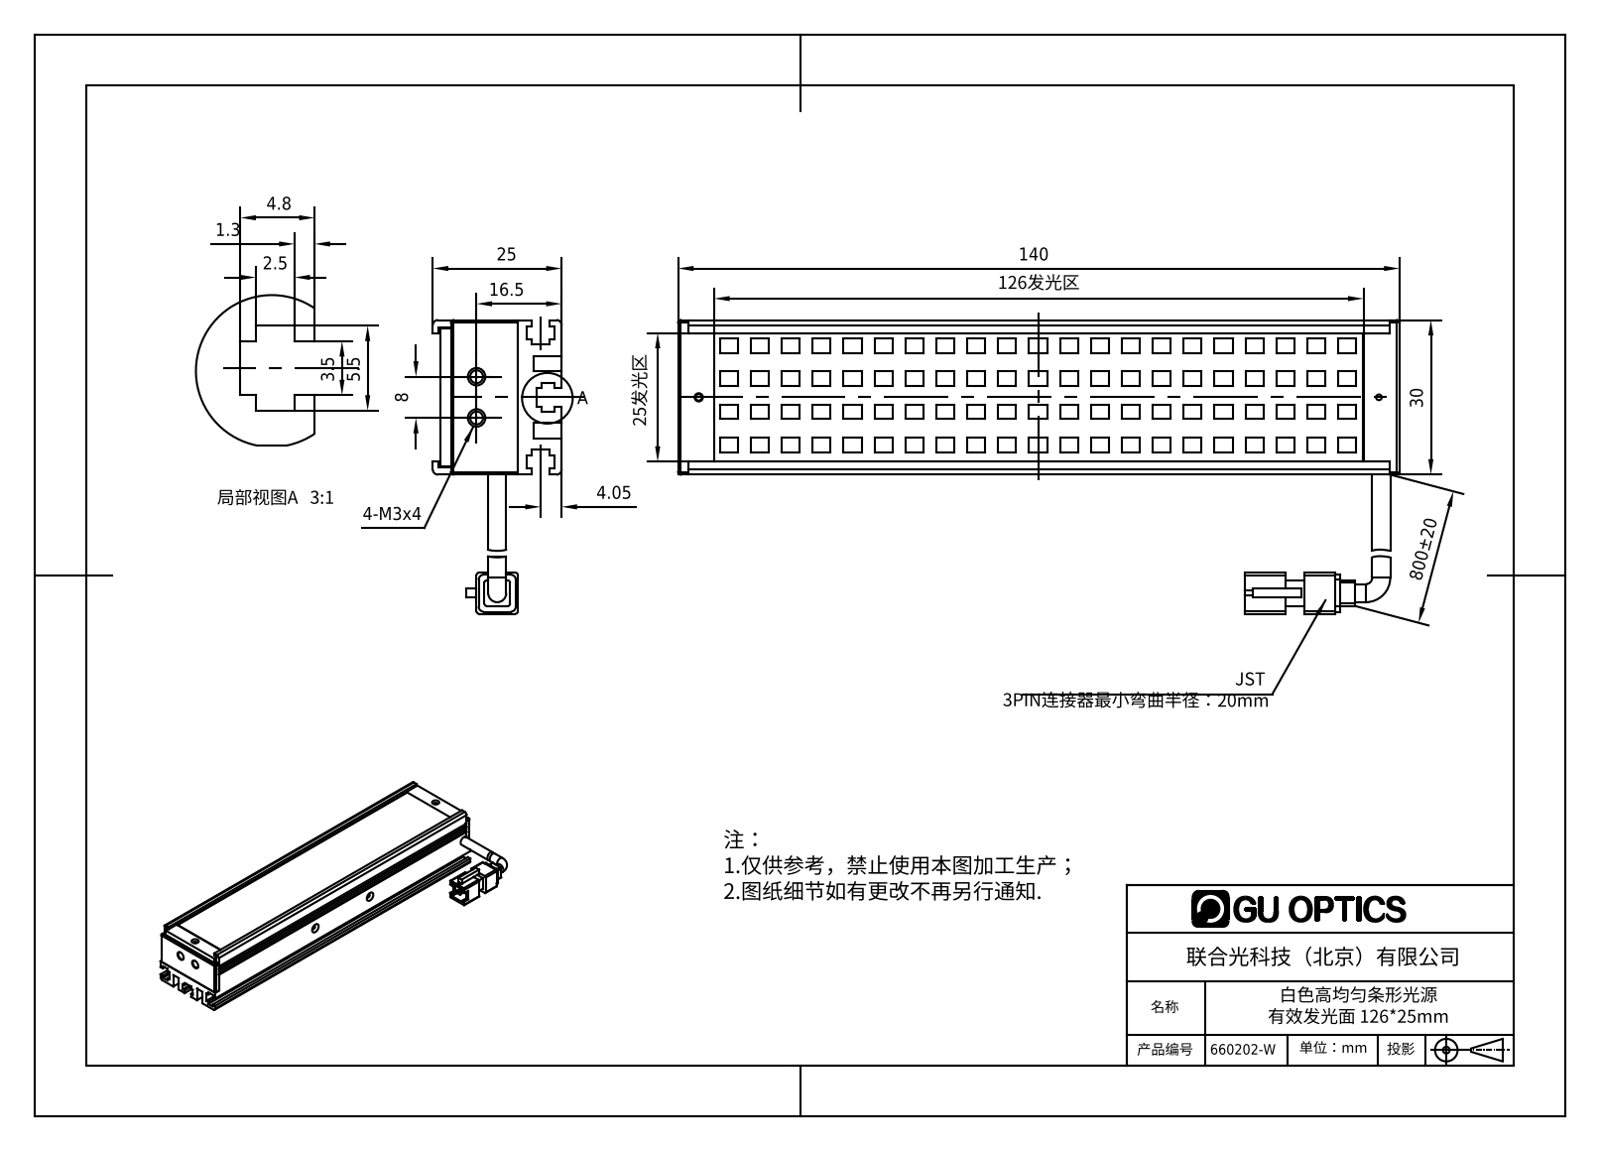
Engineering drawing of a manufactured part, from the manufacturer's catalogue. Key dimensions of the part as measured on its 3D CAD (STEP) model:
Part name (STEP PRODUCT): 660202-W
STEP written by: SolidWorks 2016 (AUTOMOTIVE_DESIGN)
Units: millimetres
Bodies: 6 solids, 864 faces (678 planar, 83 cylindrical, 103 other)
Overall size (bounding box): 140 × 57 × 25
Volume: 49 865 mm³ · Surface area: 50 427 mm²
Round holes (diameter × count): ⌀1.6 ×5, ⌀1.5 ×2, ⌀1.7 ×2, ⌀2.5 ×2, ⌀2.8 ×2, ⌀3 ×2, ⌀1.1 ×1, ⌀1.25 ×1, ⌀2 ×1
Round bosses / shafts (diameter × count): ⌀3.5 ×2
Partial cylindrical surfaces — rounded edges, fillets, slot ends (radius × count): R1 ×12, R0.5 ×8, R1.65 ×1
Main face-to-face distances: 1, 13, 2, 2.5, 3, 9.5, 27.5, 4.5, 8.5, 21.5
Hole centre spacings: 132, 7, 51, 51.43, 81, 81.27, 132.19, 8
